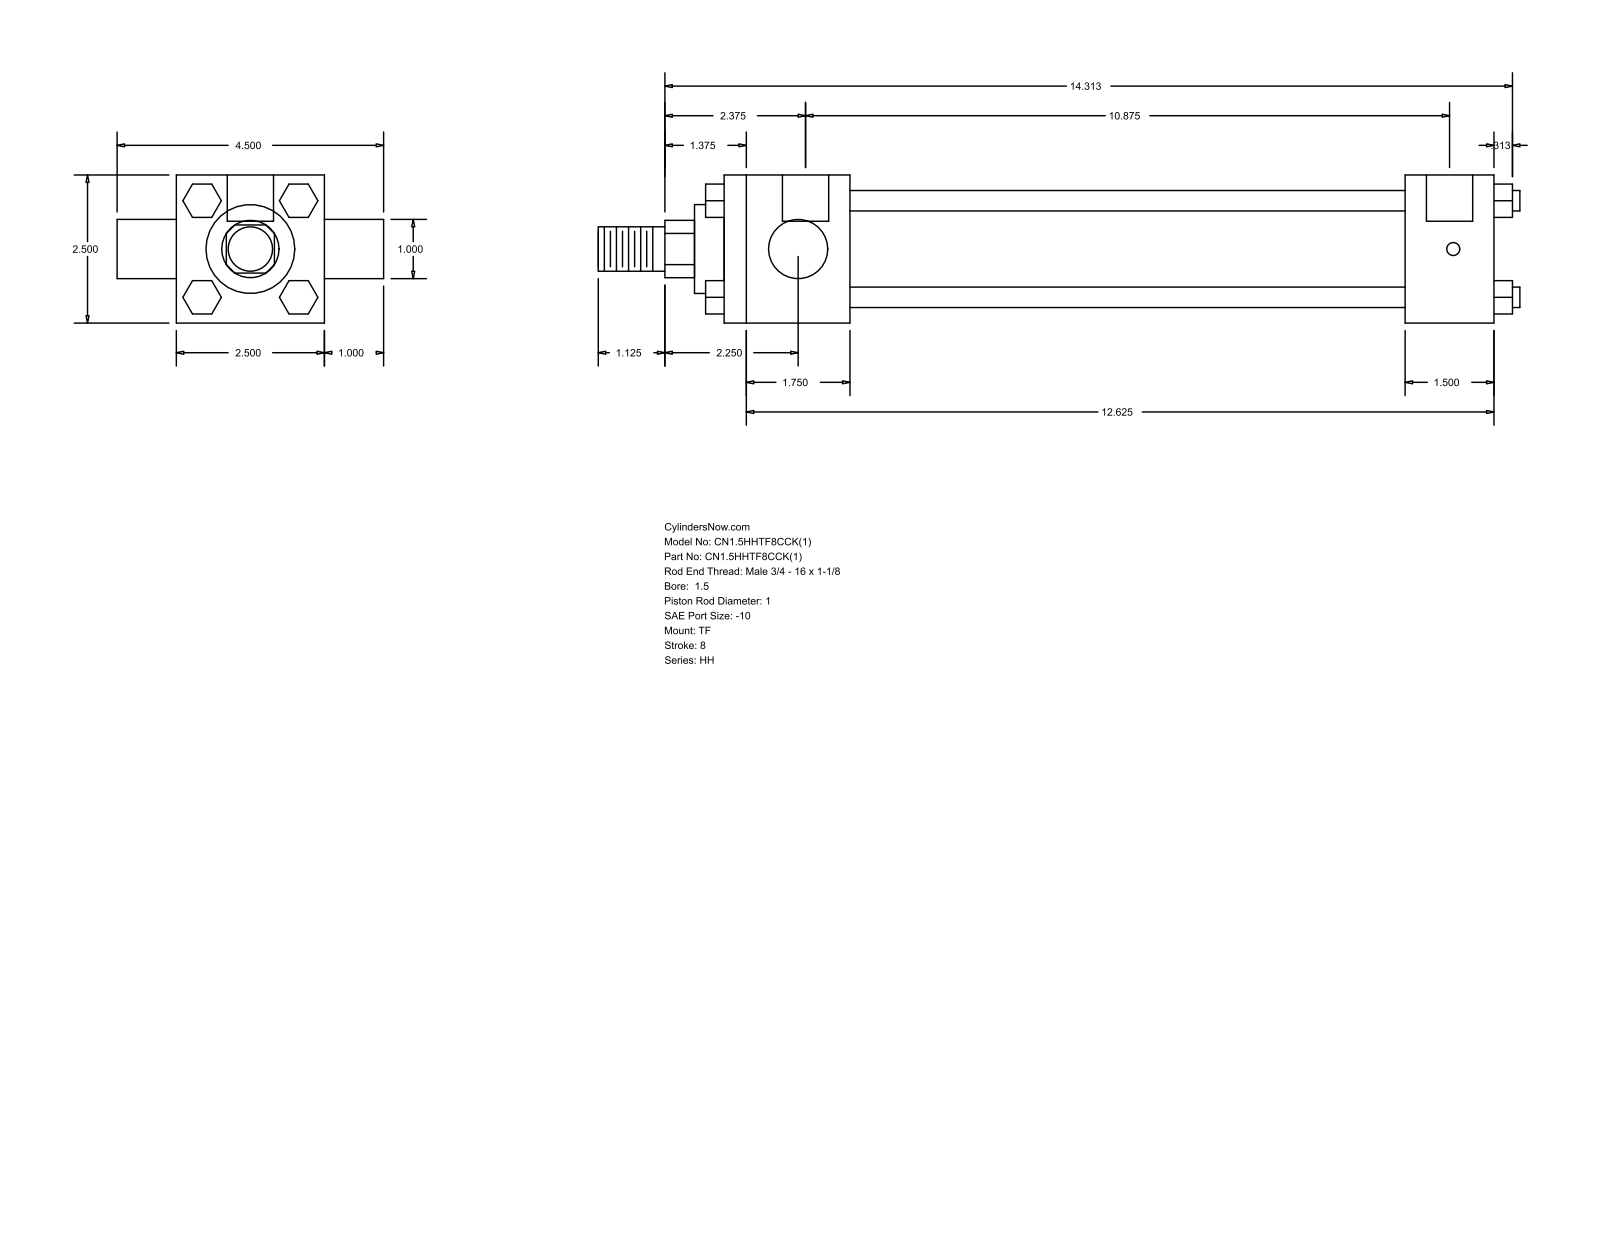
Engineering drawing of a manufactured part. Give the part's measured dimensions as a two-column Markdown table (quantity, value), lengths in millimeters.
| quantity | value |
| --- | --- |
| part name | HH_TF__0150_1 |
| STEP written by | GSSL Pune (CONFIG_CONTROL_DESIGN) |
| units | millimeters |
| bodies | 0 solids, 120 faces (92 planar, 28 cylindrical, 0 other) |
| overall size | 395.29 × 114.3 × 63.5 |
| round holes (diameter × count) | 5.56 × 3, 19.84 × 2 |
| round bosses / shafts (diameter × count) | 8.76 × 4, 25.4 × 2, 44.45 × 1, 38.1 × 1, 19.05 × 1 |
| partial cylindrical surfaces (radius × count) | 12.29 × 1 |
| main face-to-face distances | 63.5, 38.1, 276.22, 238.12, 53.98, 292.1, 330.2, 25.4, 20.7, 14.29 |
| hole center spacings | 1.59, 277.81, 276.22, 279.4 |
